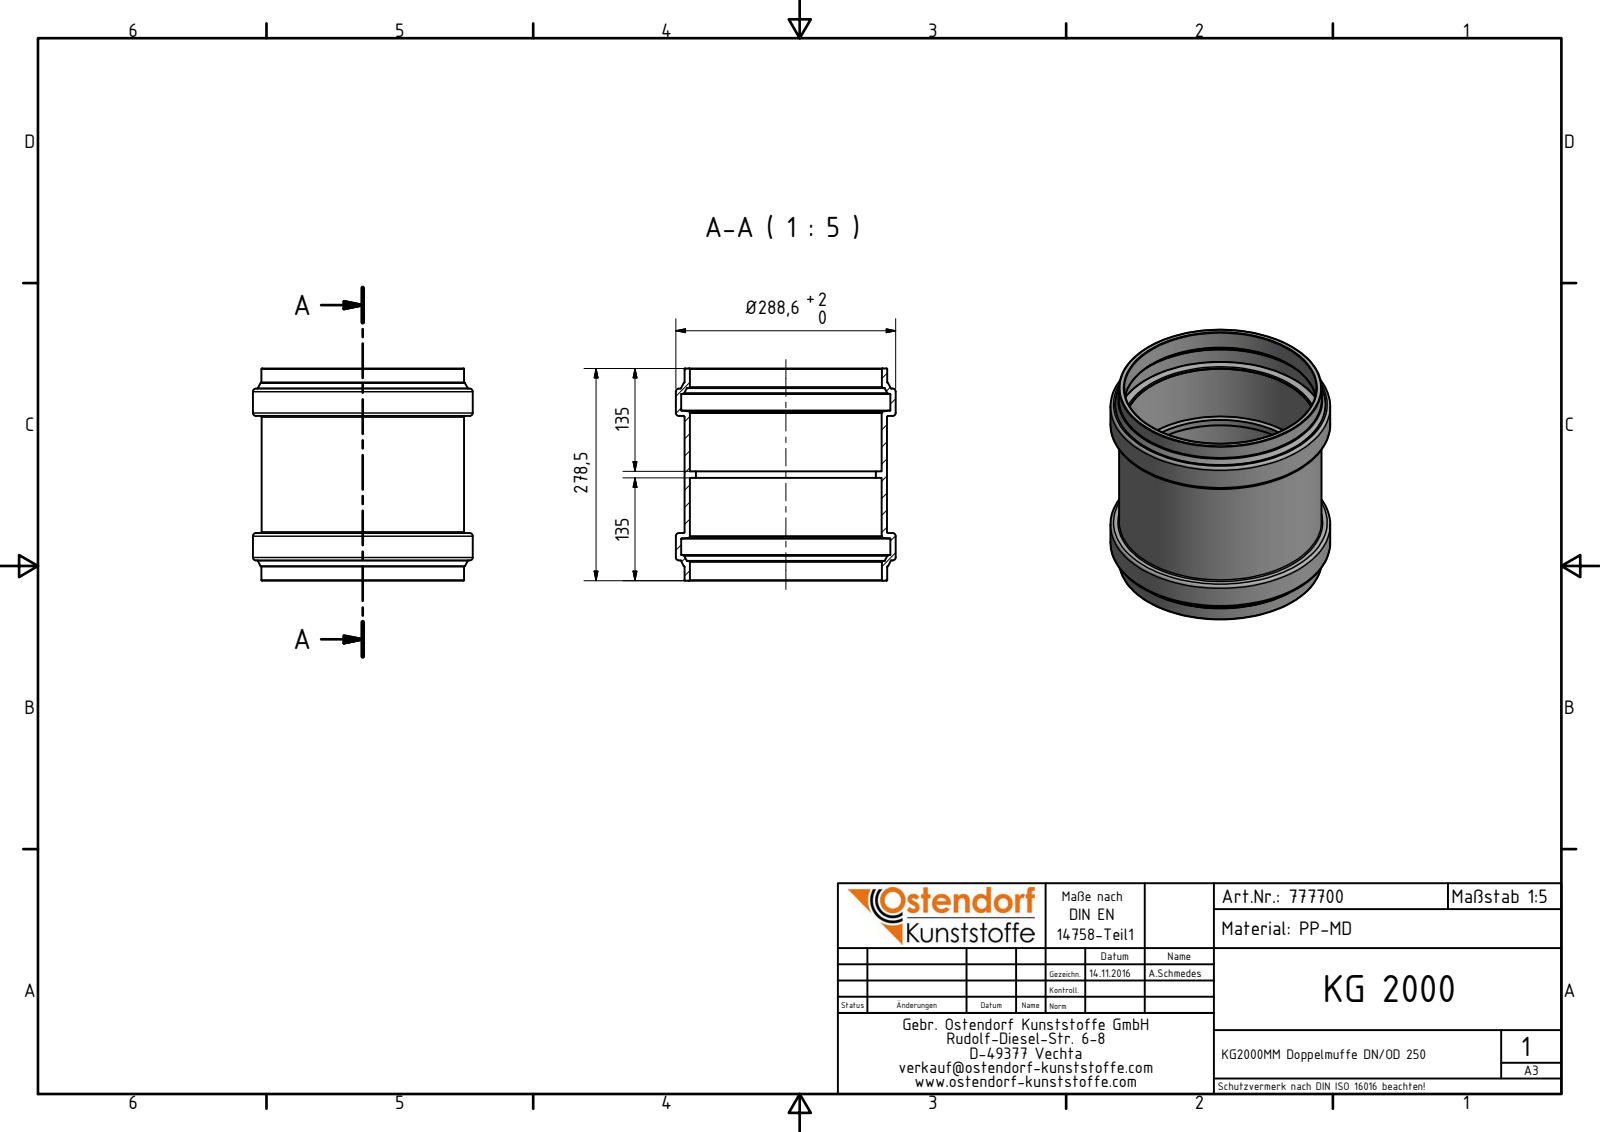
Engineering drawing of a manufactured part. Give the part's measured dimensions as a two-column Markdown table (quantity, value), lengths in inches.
| quantity | value |
| --- | --- |
| part name | 777700 KG2000MM Doppelmuffe DN_OD 250 |
| STEP written by | Autodesk Inventor 2016 (AUTOMOTIVE_DESIGN) |
| units | inches |
| bodies | 1 solid, 62 faces (10 planar, 14 cylindrical, 38 other) |
| overall size | 11.362 × 11.362 × 10.965 |
| volume | 114.5 in³ |
| surface area | 833 in² |
| round holes (diameter × count) | 9.291 × 1, 9.909 × 1, 9.925 × 1, 10.811 × 1 |
| round bosses / shafts (diameter × count) | 11.362 × 1, 10.476 × 1, 10.461 × 1 |
| main face-to-face distances | 2.858, 3.193, 2.457, 5.315, 5.65, 8.508, 0.335, 6.051, 10.965, 1.043 |
